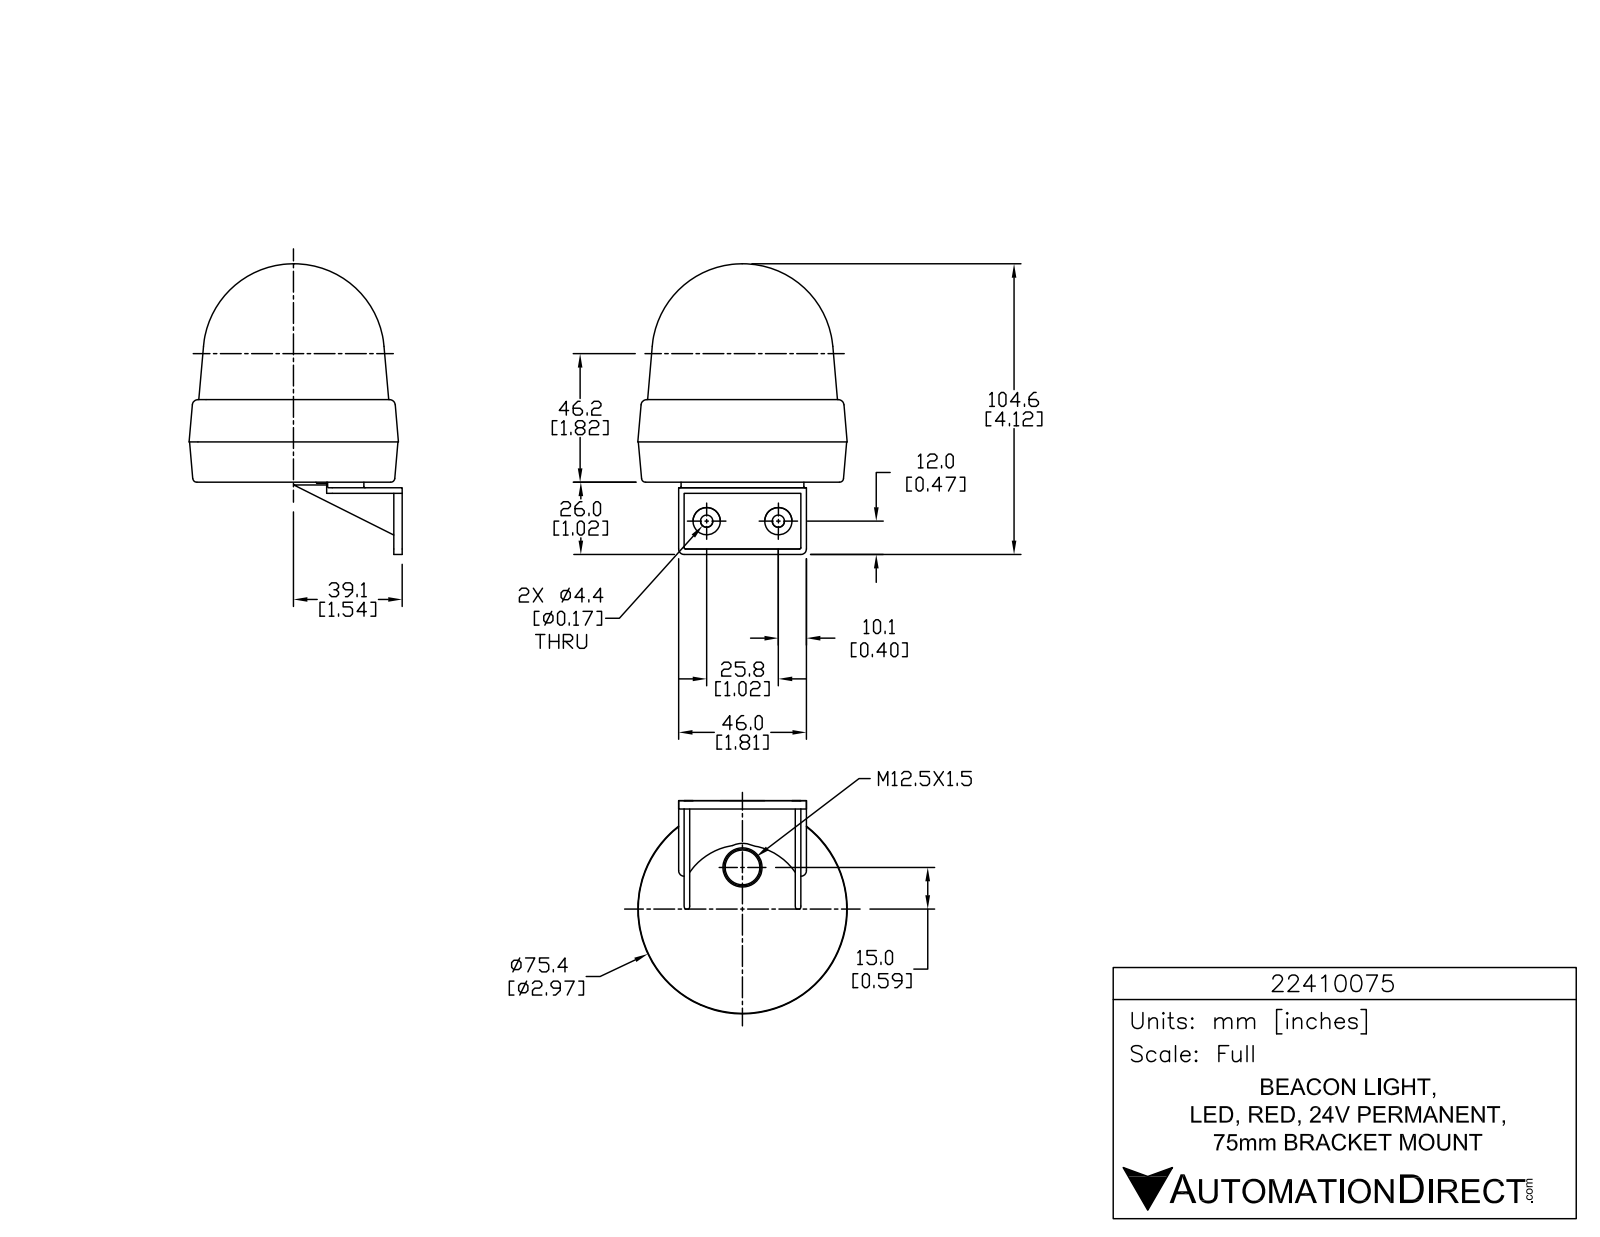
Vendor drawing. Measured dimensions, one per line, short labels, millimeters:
name: 22410075
written by: SolidWorks 2015 (AUTOMOTIVE_DESIGN)
unit: mm
bodies: 1 solid, 819 faces (549 planar, 180 cylindrical, 90 other)
size: 104.6 × 82.6 × 75.4
volume: 262 500 mm³; area: 27 080 mm²
holes: 3× ⌀1.5, 2× ⌀4.4
bosses: 3× ⌀8.6, 3× ⌀2.1, 2× ⌀9.8
rounds: 9× R0.1, 6× R0.1, 6× R0.3, 6× R0.3, 6× R0.3, 6× R0.5, 6× R5, 4× R2
face distances: 2, 4, 40, 1, 3, 42, 38, 2, 42, 44
hole spacings: 25.8
